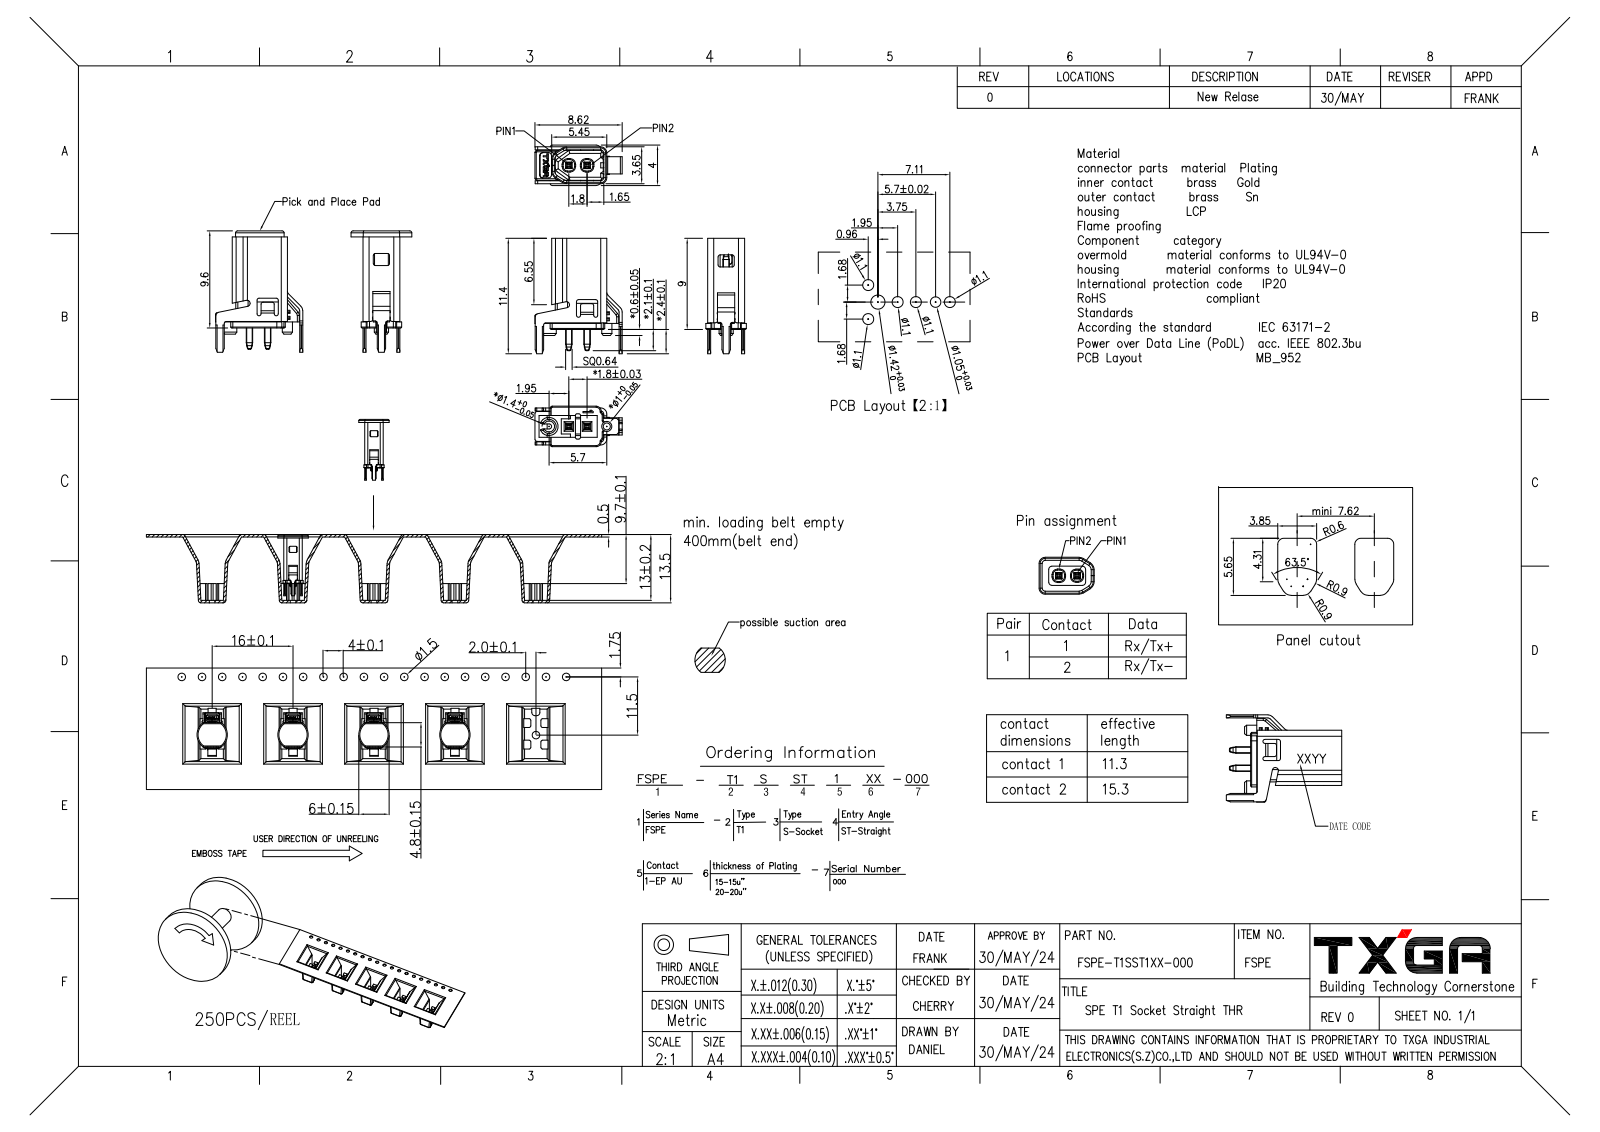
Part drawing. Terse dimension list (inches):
name: CAP_1; ST-SPE-T1_ASM_8_ASM; PRT0002; FSPE-T1SST1XX-000_ASM
written by: PRO/ENGINEER BY PARAMETRIC TECHNOLOGY CORPORATION, 2010280 (CONFIG_CONTROL_DESIGN)
unit: in
bodies: 2 solids, 701 faces (410 planar, 223 cylindrical, 68 other)
size: 0.472 × 0.339 × 0.236
volume: 0.008 in³; area: 0.969 in²
bosses: 1× ⌀0.055, 1× ⌀0.039
rounds: 35× R0.008, 31× R0.004, 14× R0.005, 12× R0.012, 12× R0.039, 11× R0.02, 8× R0.022, 7× R0.006
face distances: 0.131, 0.024, 0.047, 0.12, 0.143, 0.084, 0.059, 0.072, 0.071, 0.354
